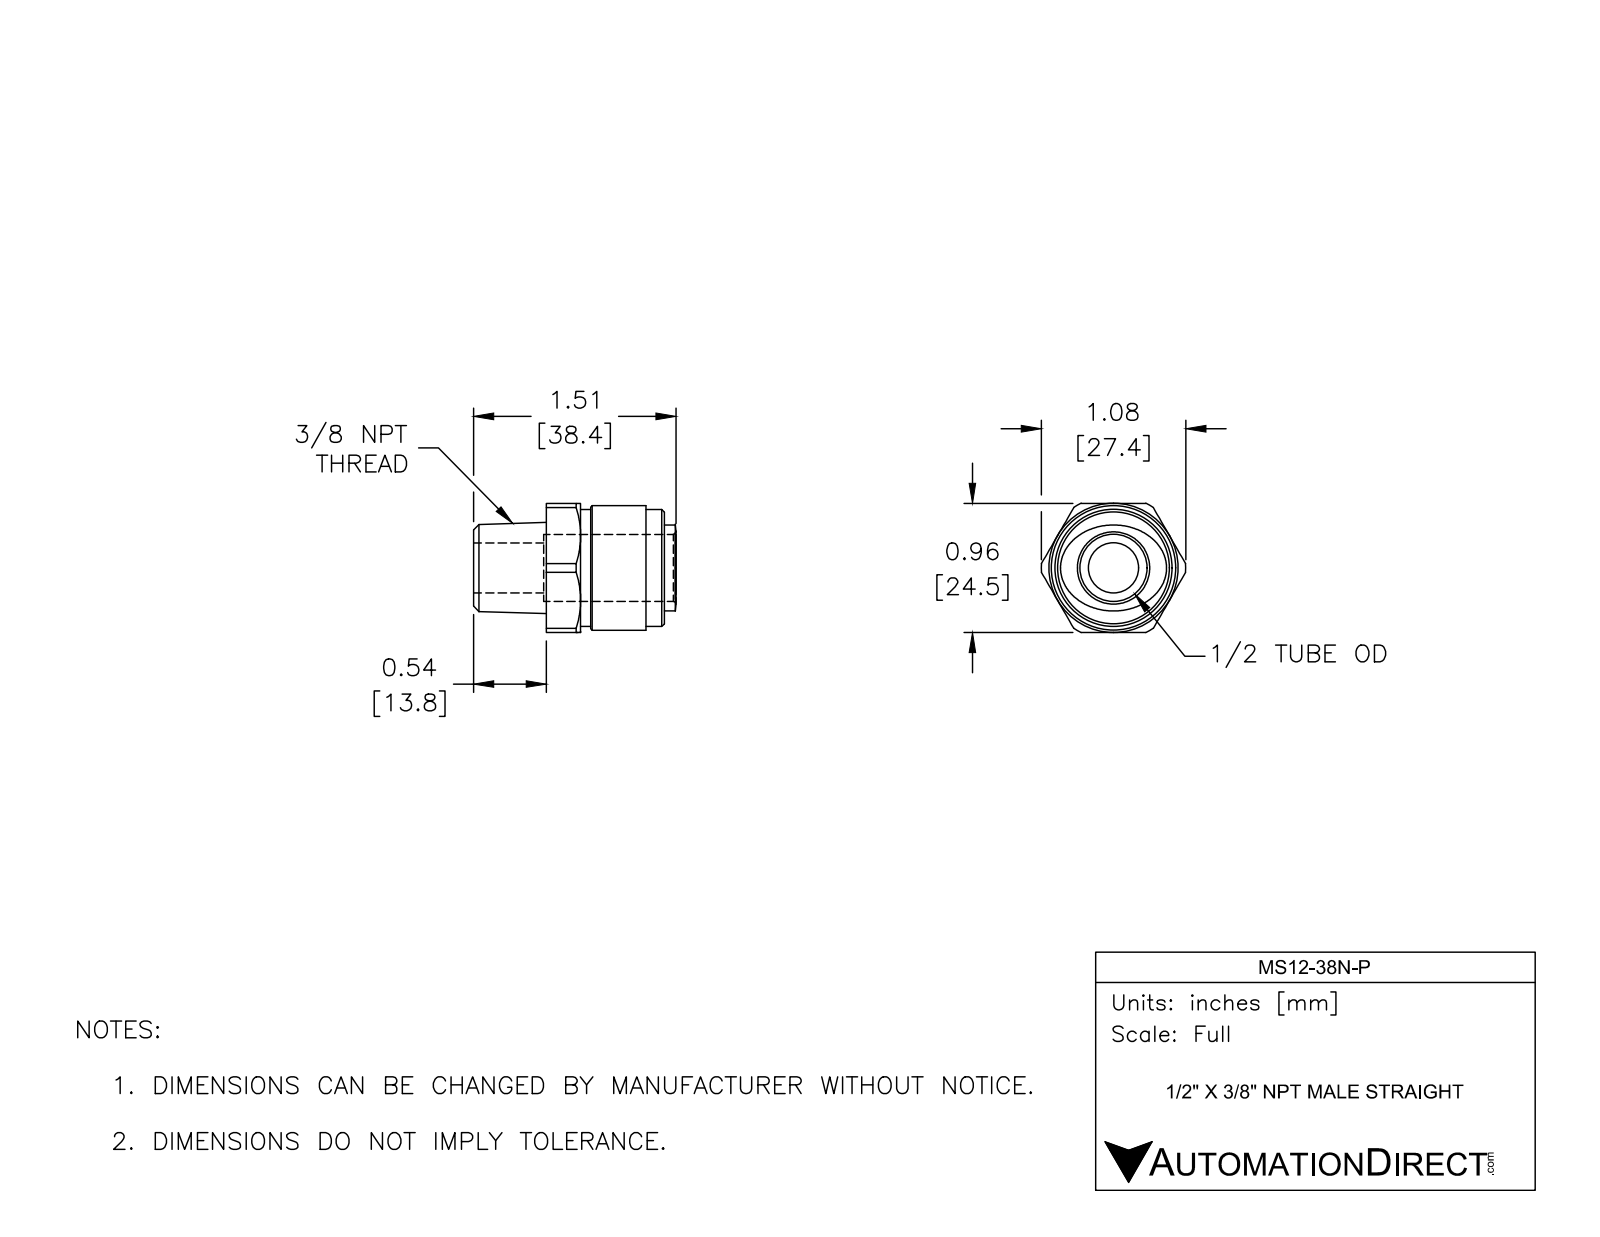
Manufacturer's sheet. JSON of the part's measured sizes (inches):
{"part_name": "MS12-38N-P", "step_written_by": "SolidWorks 2017 (AUTOMOTIVE_DESIGN)", "units": "inches", "bodies": {"solids": 1, "faces": 49, "planar": 13, "cylindrical": 16, "other": 20}, "overall_size": [1.512, 1.079, 0.965], "volume_in3": 0.58, "surface_area_in2": 7.471, "round_holes": [[0.374, 1], [0.5, 1]], "round_bosses_or_shafts": [[0.929, 1], [0.874, 1]], "partial_cylinders_radius": [[0.539, 1]], "face_to_face_distances": [0.965, 0.882, 0.543, 1.425, 0.799, 0.256, 0.626, 0.524, 0.02, 0.276]}
